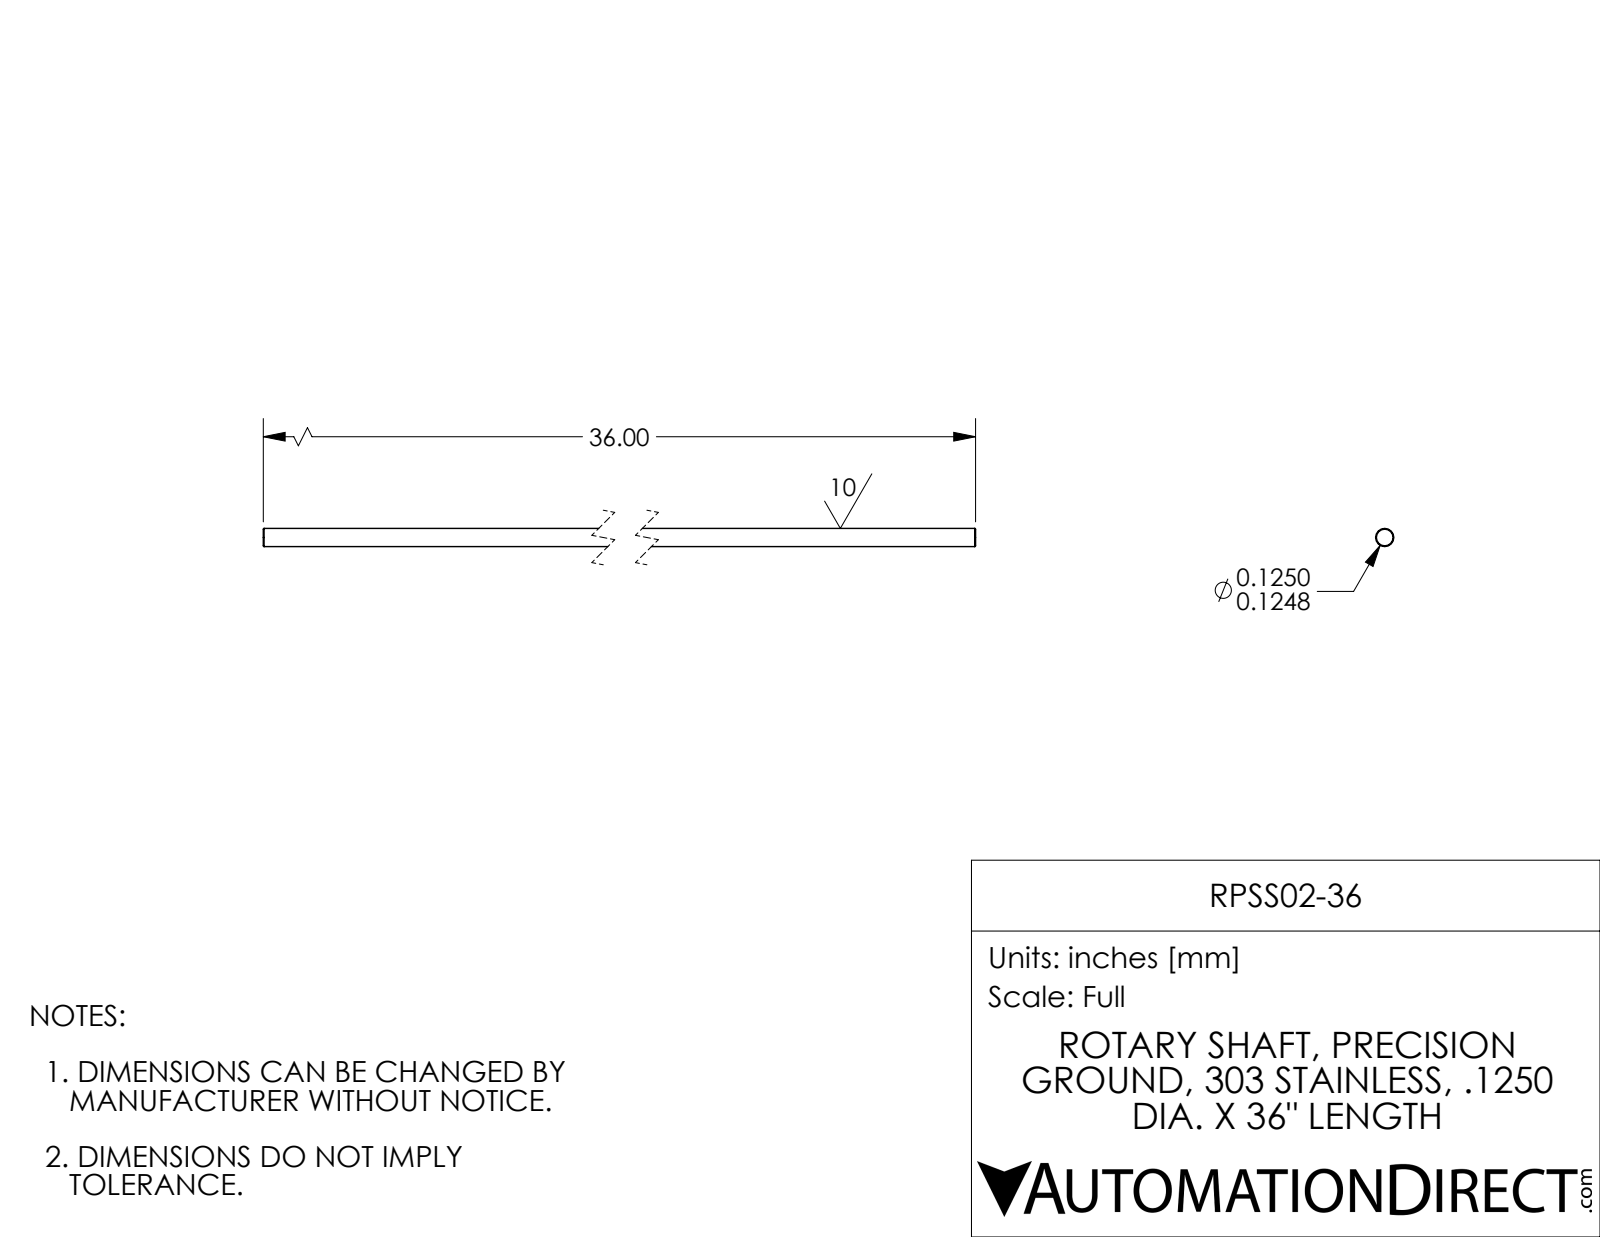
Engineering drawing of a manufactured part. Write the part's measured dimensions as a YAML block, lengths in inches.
part_name: "RPSS02-36"
step_written_by: "SolidWorks 2017 (AUTOMOTIVE_DESIGN)"
units: inches
bodies: {solids: 1, faces: 8, planar: 2, cylindrical: 2, other: 4}
overall_size: [36, 0.125, 0.125]
volume: 0.442
surface_area: 14.16
round_bosses_or_shafts:
  - {diameter: 0.125, count: 1}
face_to_face_distances: [36]
